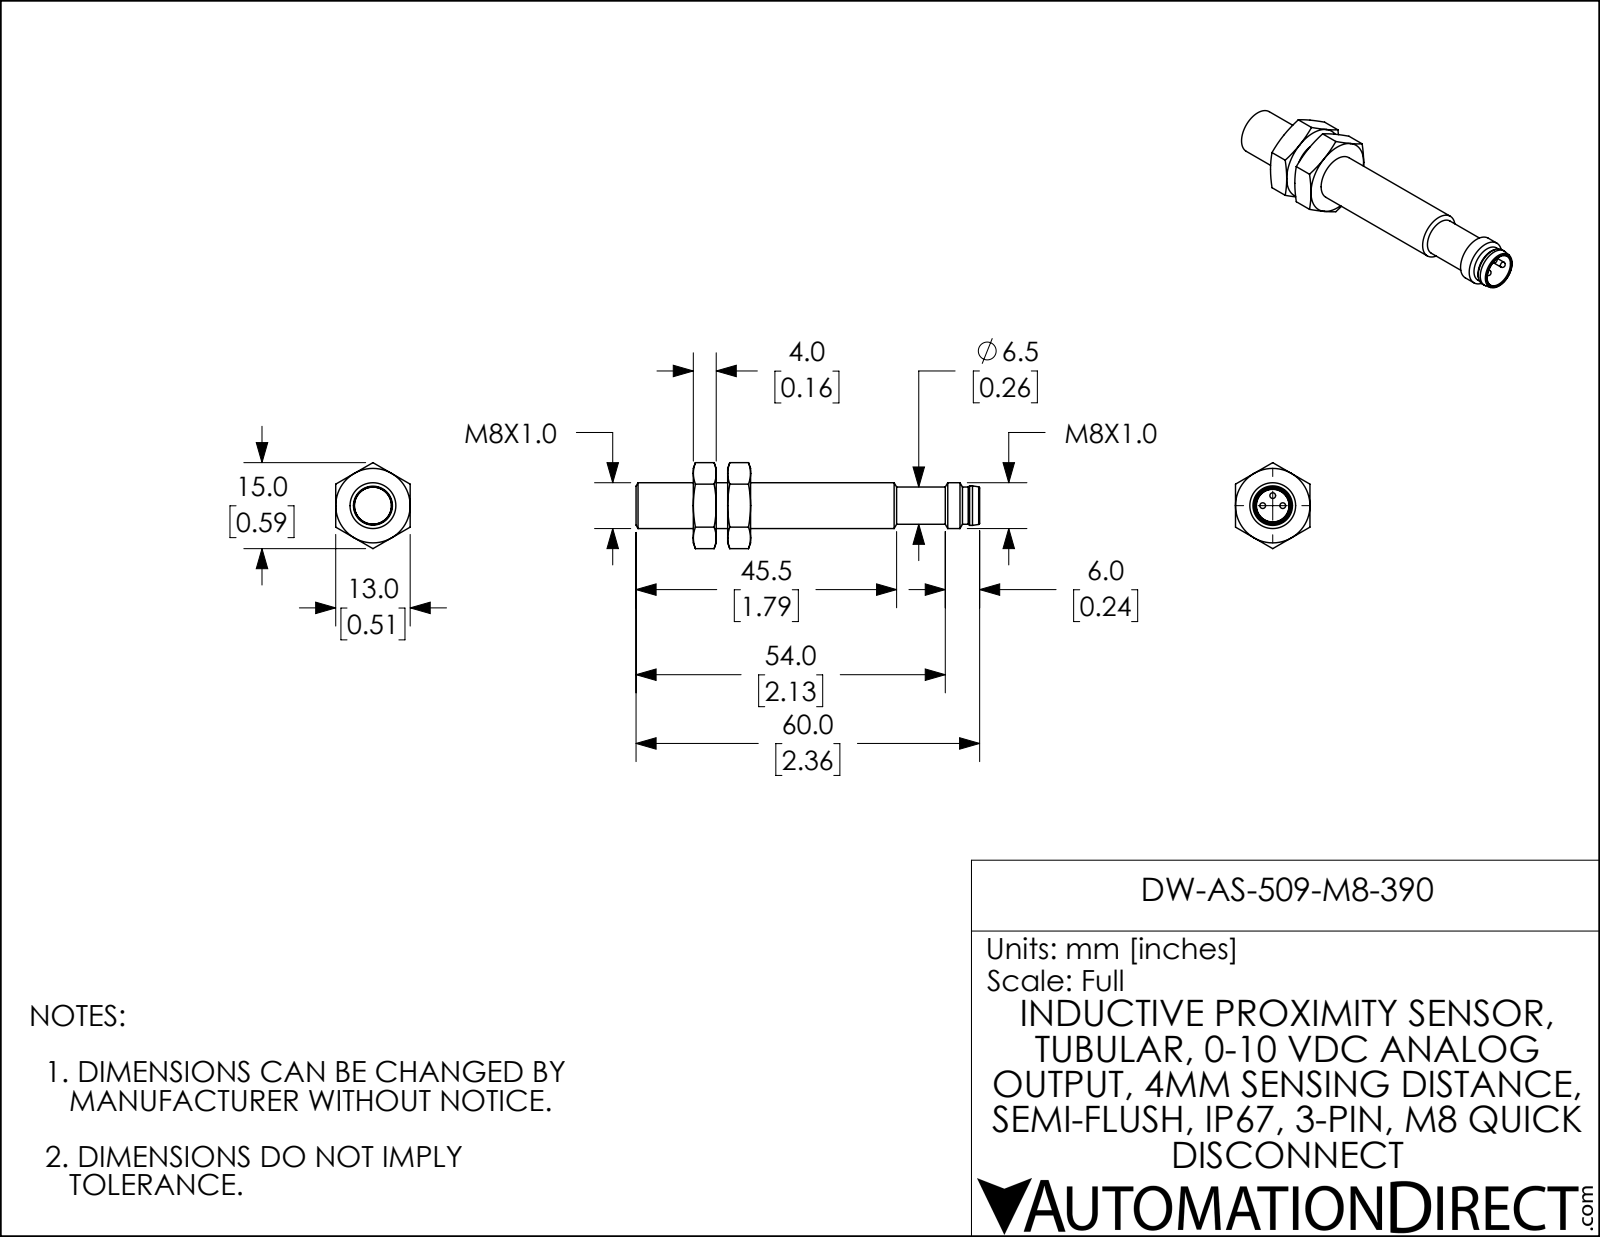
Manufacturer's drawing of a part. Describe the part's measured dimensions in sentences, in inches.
The part is named "DW-AS-509-M8-390". Its 3-D file was written by "SolidWorks 2018 (AUTOMOTIVE_DESIGN)". It is 1 solid with 71 faces: 23 planar, 13 cylindrical and 35 other. Overall it measures 2.362 by 0.591 by 0.512 inches. Its volume is 0.211 cubic inches and its surface area 3.492 square inches. Round holes: 1 of diameter 0.228. Round bosses or shafts: 3 of diameter 0.039, 1 of diameter 0.315, 1 of diameter 0.272, 1 of diameter 0.256, 1 of diameter 0.255, 1 of diameter 0.224. The main face-to-face distances are 0.512, 0.236, 0.157, 0.394, 0.079, 0.551, 0.63, 0.787, 1.772, 1.535.
